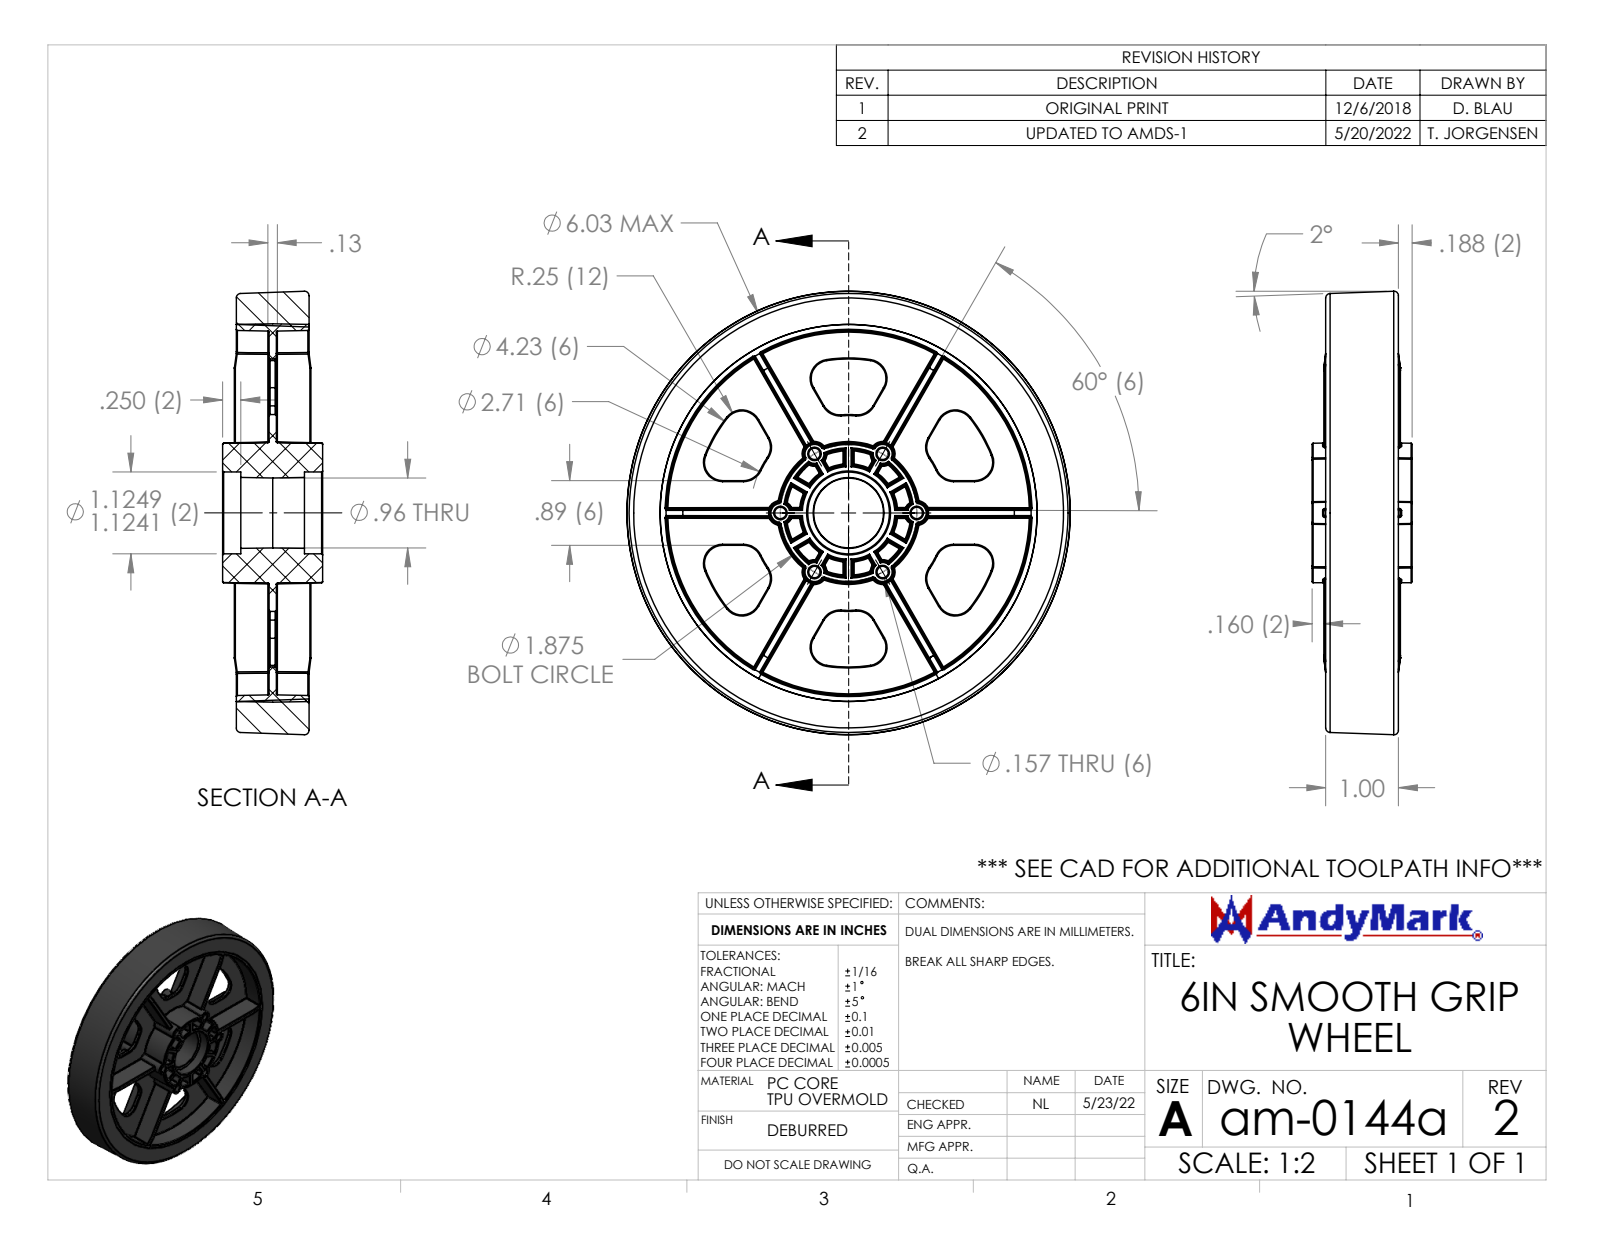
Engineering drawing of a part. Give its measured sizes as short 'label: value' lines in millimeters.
name: 6 wheel Rev 4; SmoothGrip Tread; am-0144a SmoothGrip Wheel
written by: SolidWorks 2021 (CONFIG_CONTROL_DESIGN)
unit: mm
bodies: 2 solids, 1583 faces (153 planar, 265 cylindrical, 1165 other)
size: 154.8 × 154.8 × 34.9
volume: 224 700 mm³; area: 103 000 mm²
holes: 6× ⌀4, 1× ⌀28.6
rounds: 151× R0.4, 24× R6.4, 1× R34.4, 1× R53.7
face distances: 11.4, 14, 2.5, 3.3, 25.4, 3.1, 4.7, 16.2, 18.7, 30.1
hole spacings: 23.8, 41.2, 47.6, 23.8
